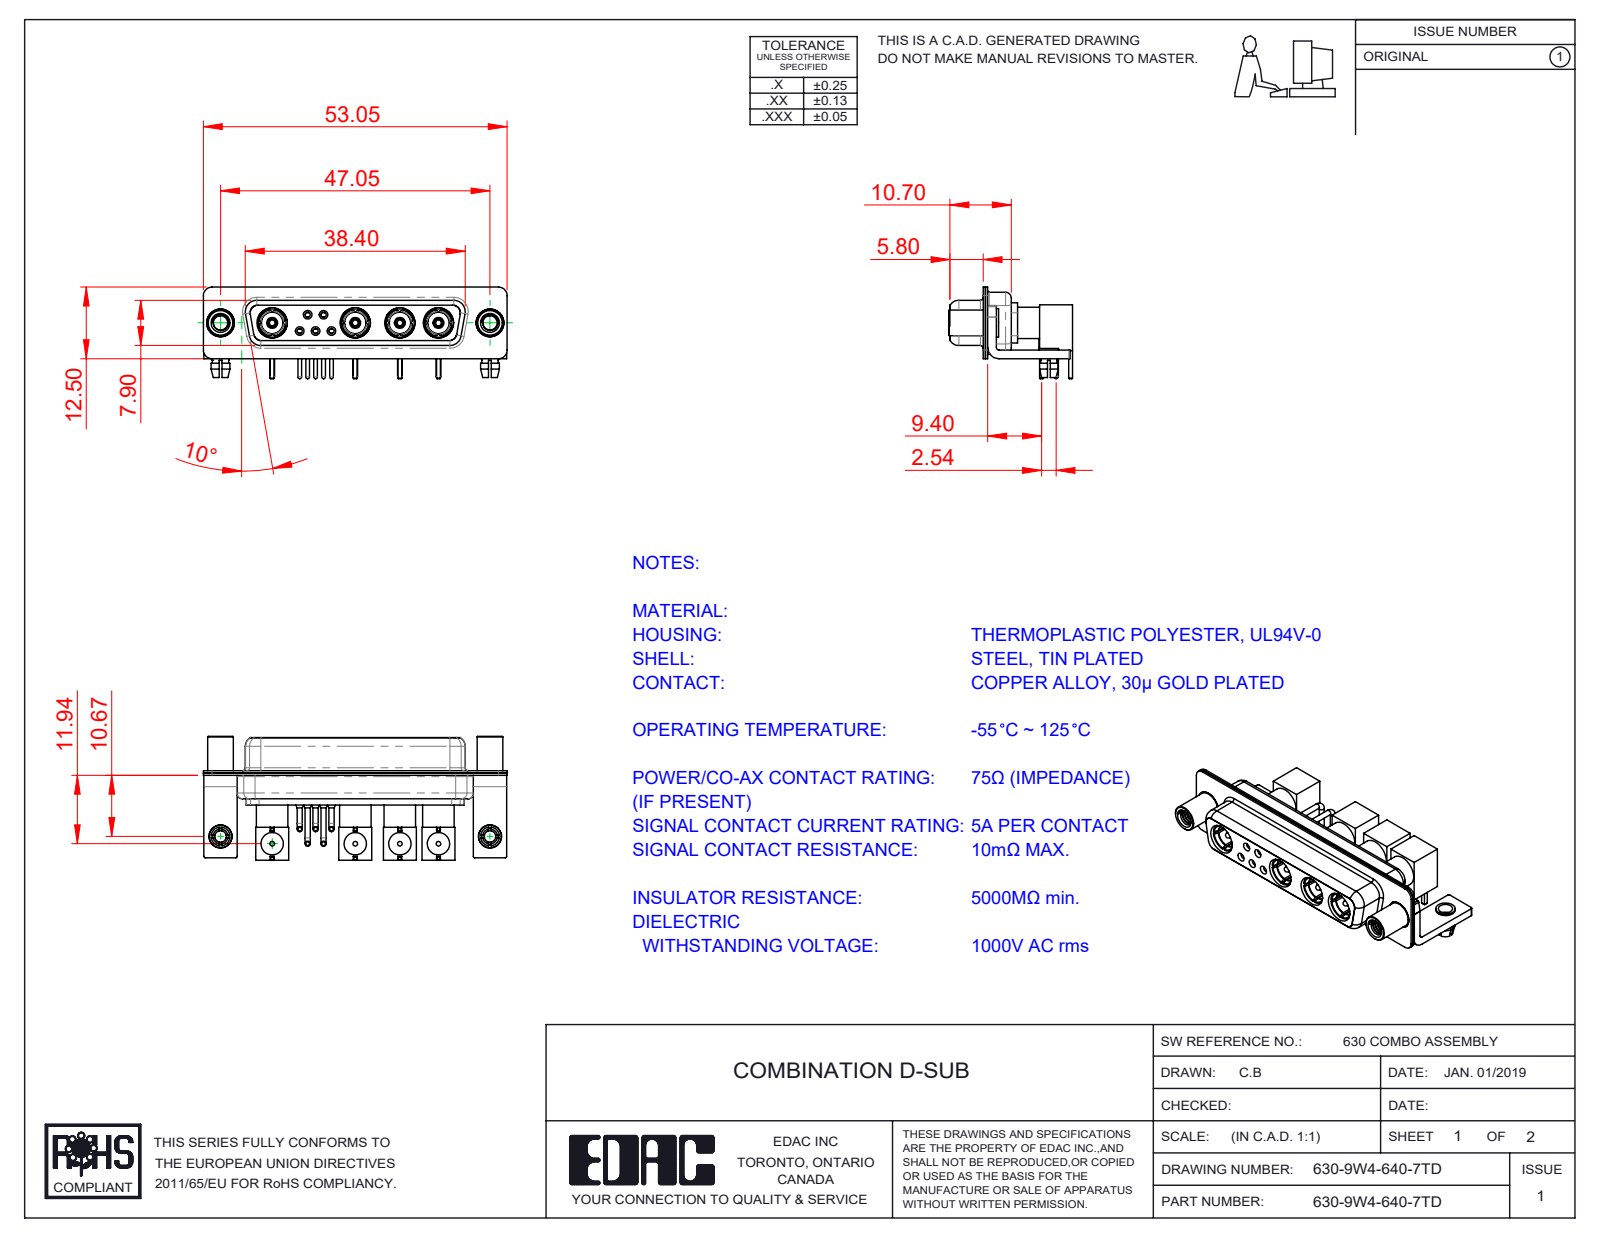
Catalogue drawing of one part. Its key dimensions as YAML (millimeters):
part_name: "630Combo Threaded Standoff_D; 630Combo Board Lock; Insulator Pin_Straight PC Tail; 630Combo Contact Row 2 (+8 more)"
step_written_by: "SolidWorks 2020 (CONFIG_CONTROL_DESIGN)"
units: millimeters
bodies: {solids: 38, faces: 1406, planar: 480, cylindrical: 616, other: 310}
overall_size: [53.05, 21.61, 16]
volume: 5106
surface_area: 12466
round_holes:
  - {diameter: 1.1, count: 9}
  - {diameter: 1.5, count: 9}
  - {diameter: 2, count: 7}
  - {diameter: 4.85, count: 6}
  - {diameter: 0.9, count: 5}
  - {diameter: 0.8, count: 4}
  - {diameter: 2.5, count: 4}
  - {diameter: 2.83, count: 4}
  - {diameter: 3.1, count: 4}
  - {diameter: 3.3, count: 4}
  - {diameter: 3.9, count: 4}
  - {diameter: 3.92, count: 4}
round_bosses_or_shafts:
  - {diameter: 5, count: 6}
  - {diameter: 4, count: 6}
  - {diameter: 2.9, count: 6}
  - {diameter: 0.9, count: 5}
  - {diameter: 0.8, count: 5}
  - {diameter: 0.65, count: 5}
  - {diameter: 5.5, count: 4}
  - {diameter: 5.2, count: 4}
partial_cylinders:
  - {radius: 0.25, count: 16}
  - {radius: 1.5, count: 16}
  - {radius: 2, count: 13}
  - {radius: 1.35, count: 8}
  - {radius: 1.6, count: 8}
  - {radius: 0.5, count: 5}
  - {radius: 0.6, count: 4}
  - {radius: 0.65, count: 4}
face_to_face_distances: [0.4, 1.4, 1.8, 0.45, 0.8, 8.45, 8.9, 1.35, 1.85, 7.05]
hole_center_spacings: [3.16, 6.74, 7.79, 14.51, 14.52, 14.53, 22.3, 29.04]
